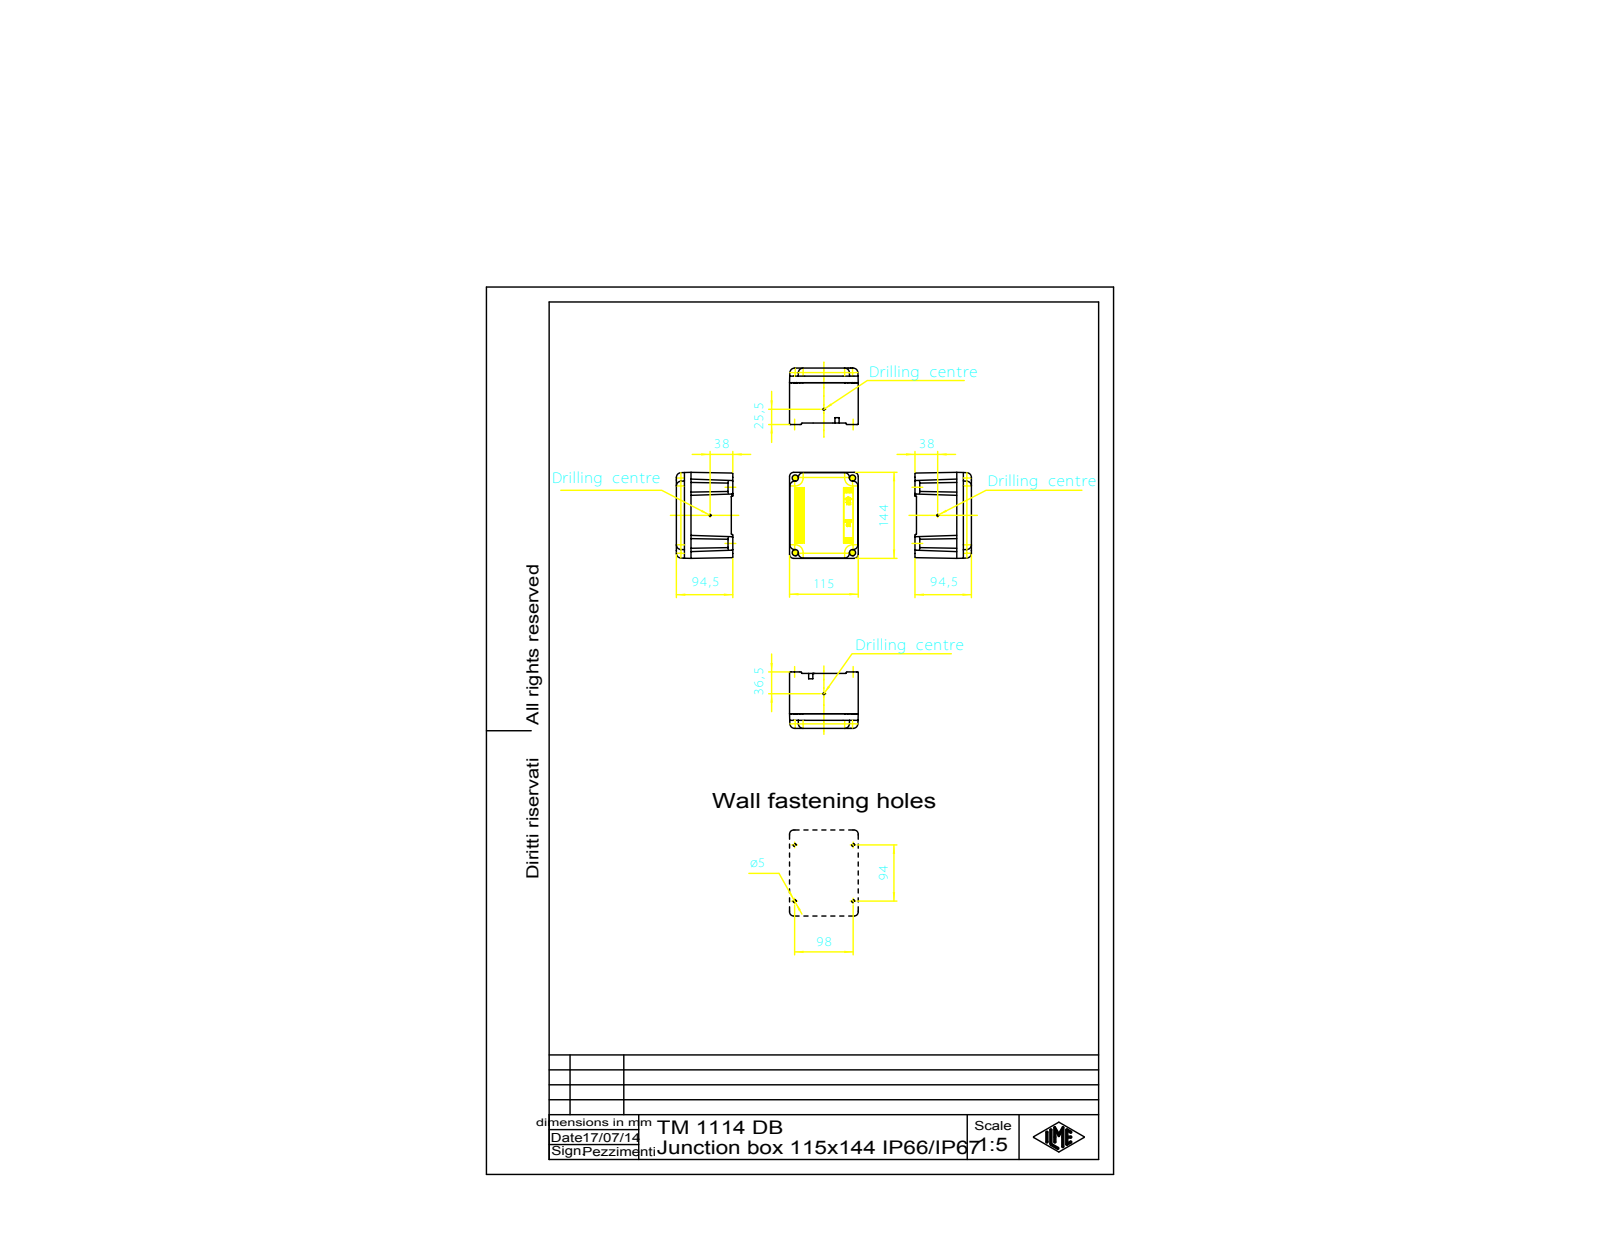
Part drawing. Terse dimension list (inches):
name: SCATOLA; COPERCHIO; TM_1114_DB
written by: Creo Elements/Direct Modeling 20.1B 02-Apr-2019 (C) Parametric Technology GmbH (AUTOMOTIVE_DESIGN)
unit: in
bodies: 2 solids, 1039 faces (763 planar, 214 cylindrical, 62 other)
size: 5.669 × 4.528 × 3.736
volume: 26.56 in³; area: 254.7 in²
holes: 4× ⌀0.11, 4× ⌀0.205
bosses: 4× ⌀0.335, 4× ⌀0.197
rounds: 80× R0.008, 16× R0.138, 16× R0.315, 11× R0.01, 8× R0.106, 8× R0.118, 8× R0.276, 8× R0.374
face distances: 0.197, 3.425, 3.622, 3.228, 0.157, 2.461, 0.965, 2.657, 0.768, 0.609
hole spacings: 2.489, 4.202, 0.922, 1.9, 3.127, 3.282, 3.78, 4.388
